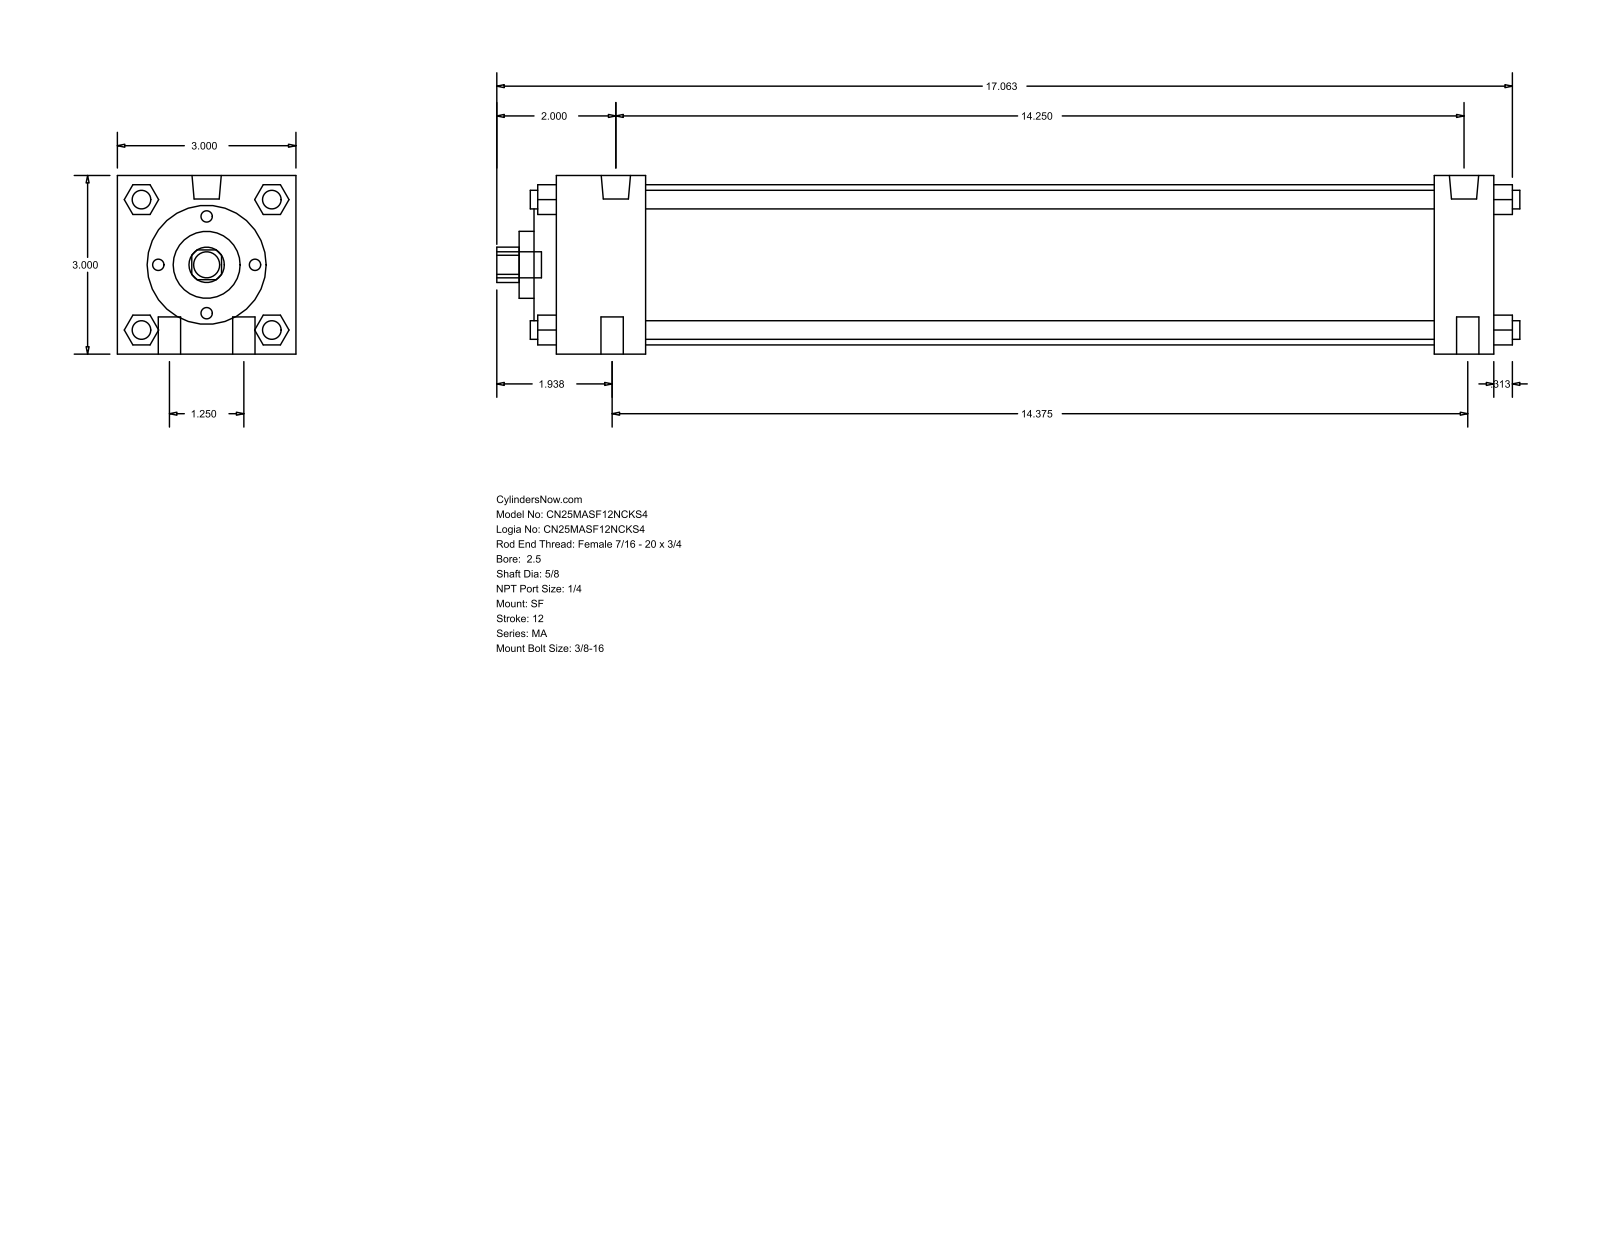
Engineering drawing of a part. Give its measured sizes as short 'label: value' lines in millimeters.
name: MA_SF__0250_0.625
written by: GSSL Pune (CONFIG_CONTROL_DESIGN)
unit: mm
bodies: 0 solids, 126 faces (95 planar, 31 cylindrical, 0 other)
size: 436.56 × 76.2 × 76.2
holes: 1× ⌀15.88, 1× ⌀28.57, 1× ⌀50.8, 1× ⌀68.33
bosses: 6× ⌀7.94, 4× ⌀9.53, 2× ⌀12.49, 1× ⌀11.11
rounds: 1× R7.54
face distances: 76.2, 400.05, 25.4, 374.65, 38.1, 336.55, 361.95, 12.7, 9.52, 47.62
